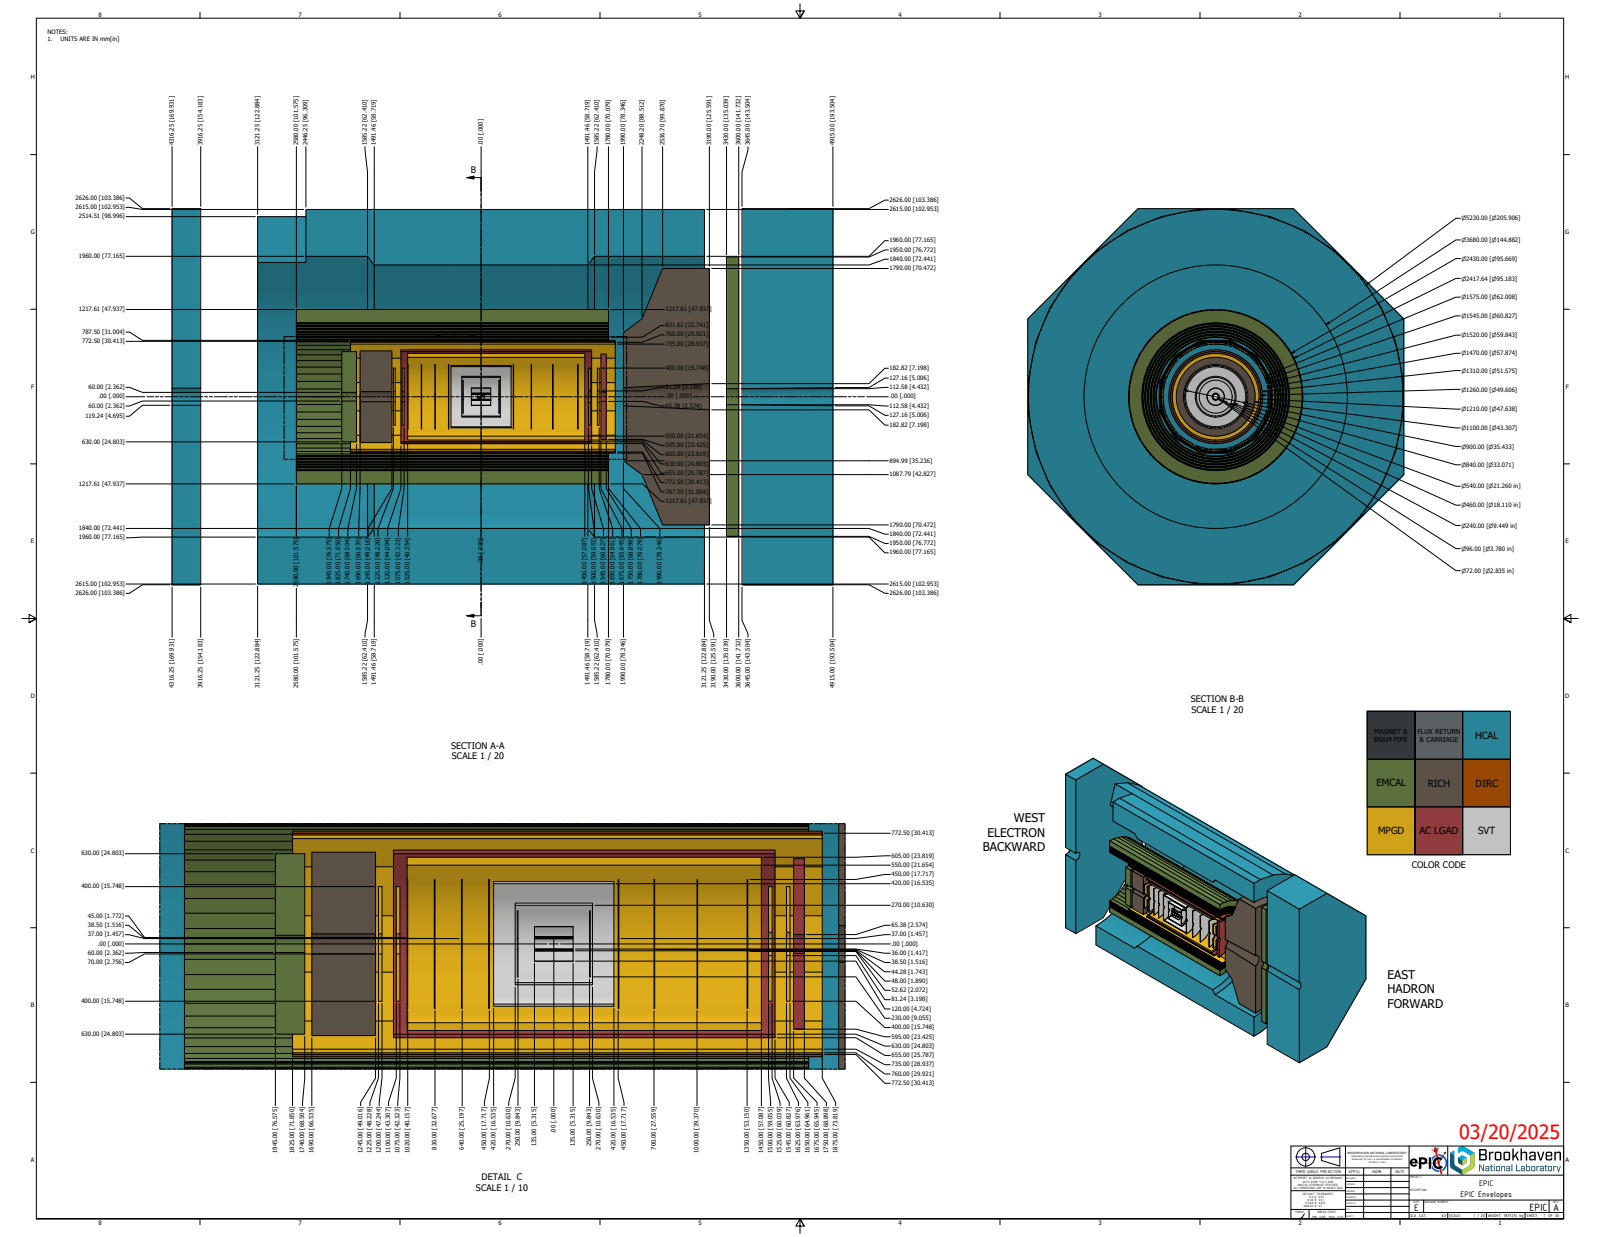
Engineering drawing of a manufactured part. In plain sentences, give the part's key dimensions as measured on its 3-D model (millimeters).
The part is named "EPIC; HCal Barrel; EMCal Barrel; DIRC (+8 more)". Its 3-D file was written by "Autodesk Inventor 2024 (AUTOMOTIVE_DESIGN)". It is 43 solids with 1415 faces: 1353 planar, 56 cylindrical and 6 other. Overall it measures 9231.25 by 5252 by 5252 millimeters. Its volume is 124 000 000 000 cubic millimeters and its surface area 1 145 000 000 square millimeters. Round holes: 2 of diameter 90, 2 of diameter 140, 1 of diameter 72, 1 of diameter 74, 1 of diameter 77, 1 of diameter 96, 1 of diameter 110, 1 of diameter 170, 1 of diameter 240, 1 of diameter 250, 1 of diameter 260, 1 of diameter 540. Round bosses or shafts: 1 of diameter 3900, 1 of diameter 3580, 1 of diameter 1310, 1 of diameter 1280, 1 of diameter 1210, 1 of diameter 1190, 1 of diameter 900, 1 of diameter 870. Partial cylindrical surfaces (rounded edges, fillets, slot ends): 2 of radius 60, 1 of radius 70. The main face-to-face distances are 11, 38.73, 27.73, 38.72, 5.95, 10.99, 400, 7561.25, 7961.25, 1270. The hole center spacings are 8, 9, 16, 17, 25, 37.5, 40, 45.5.
